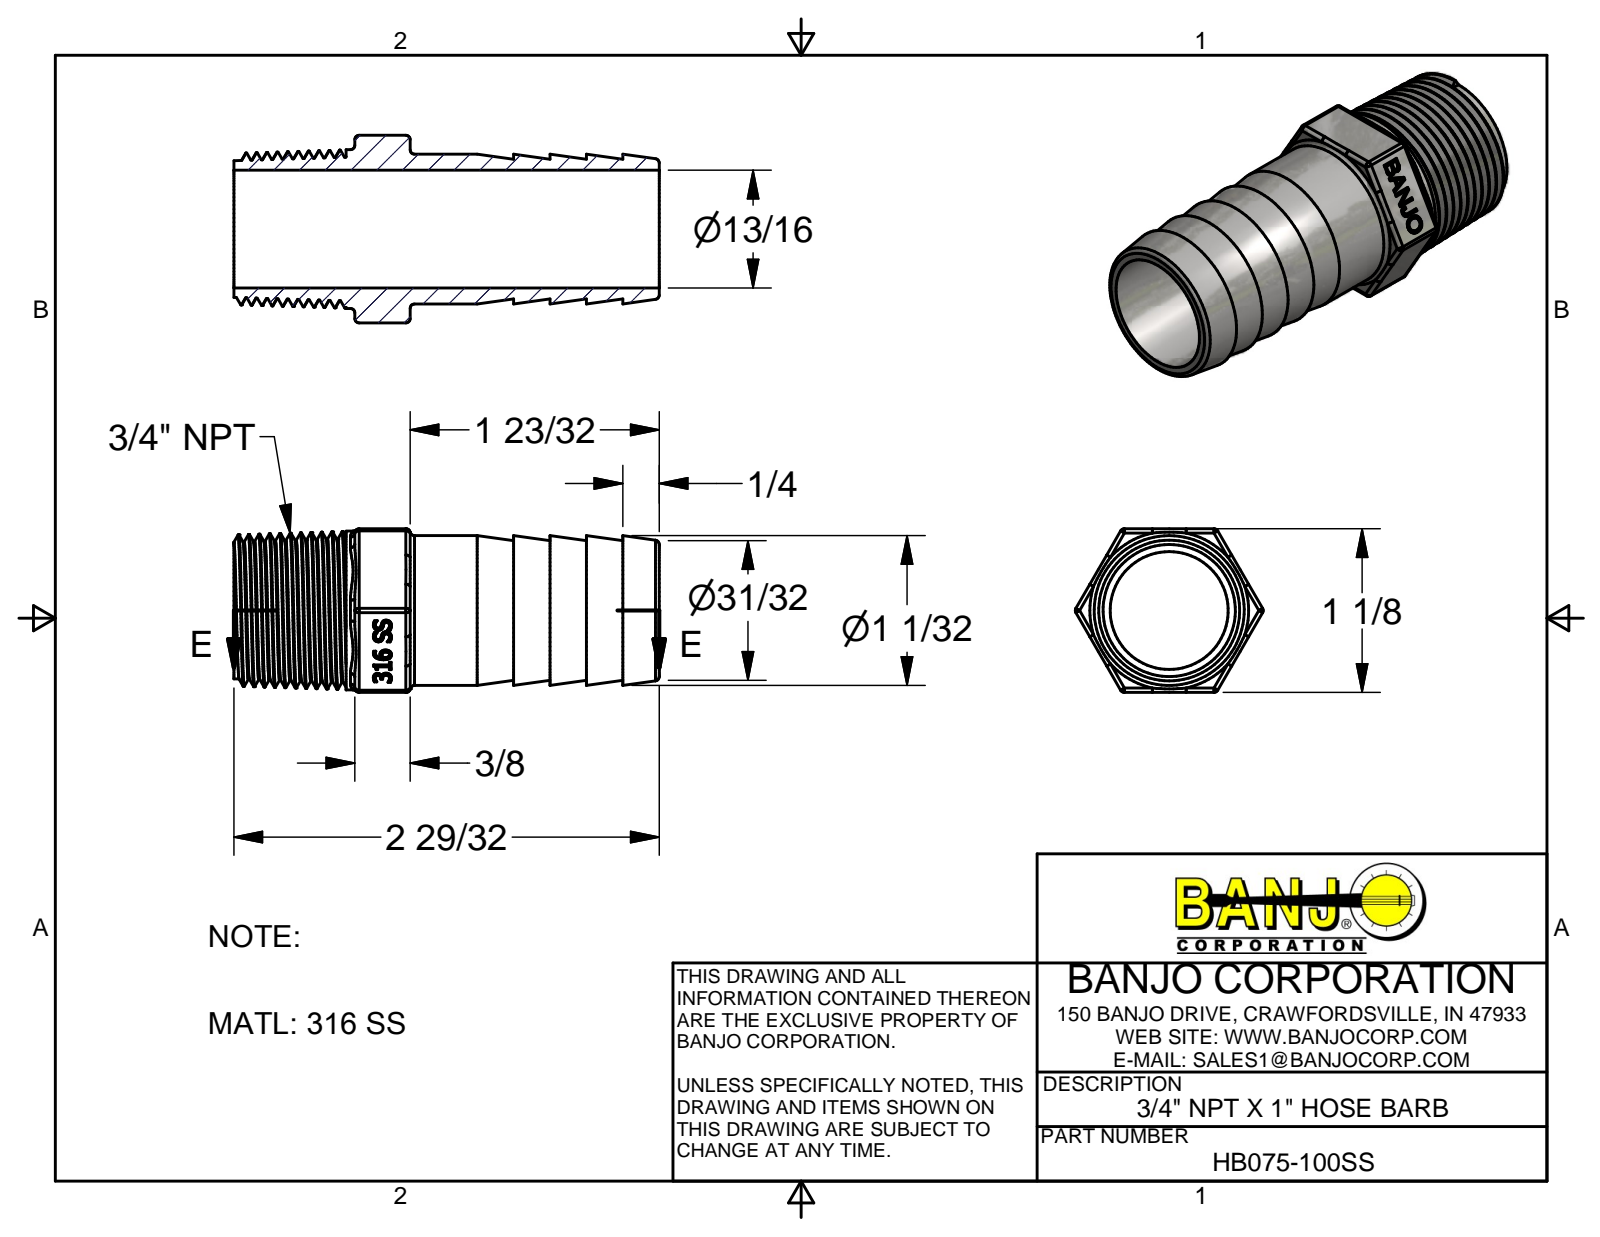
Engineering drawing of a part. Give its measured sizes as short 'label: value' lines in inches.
name: HB075-100SS
written by: Autodesk Inventor 2013 (AUTOMOTIVE_DESIGN)
unit: in
bodies: 1 solid, 274 faces (105 planar, 27 cylindrical, 142 other)
size: 2.92 × 1.29 × 1.125
volume: 0.94 in³; area: 20.14 in²
holes: 1× ⌀0.81
bosses: 1× ⌀1.092, 1× ⌀1.03
rounds: 18× R0.03
face distances: 1.125, 0.25, 0.5, 0.75, 2.92, 1, 2.67, 2.42, 2.17, 1.92
